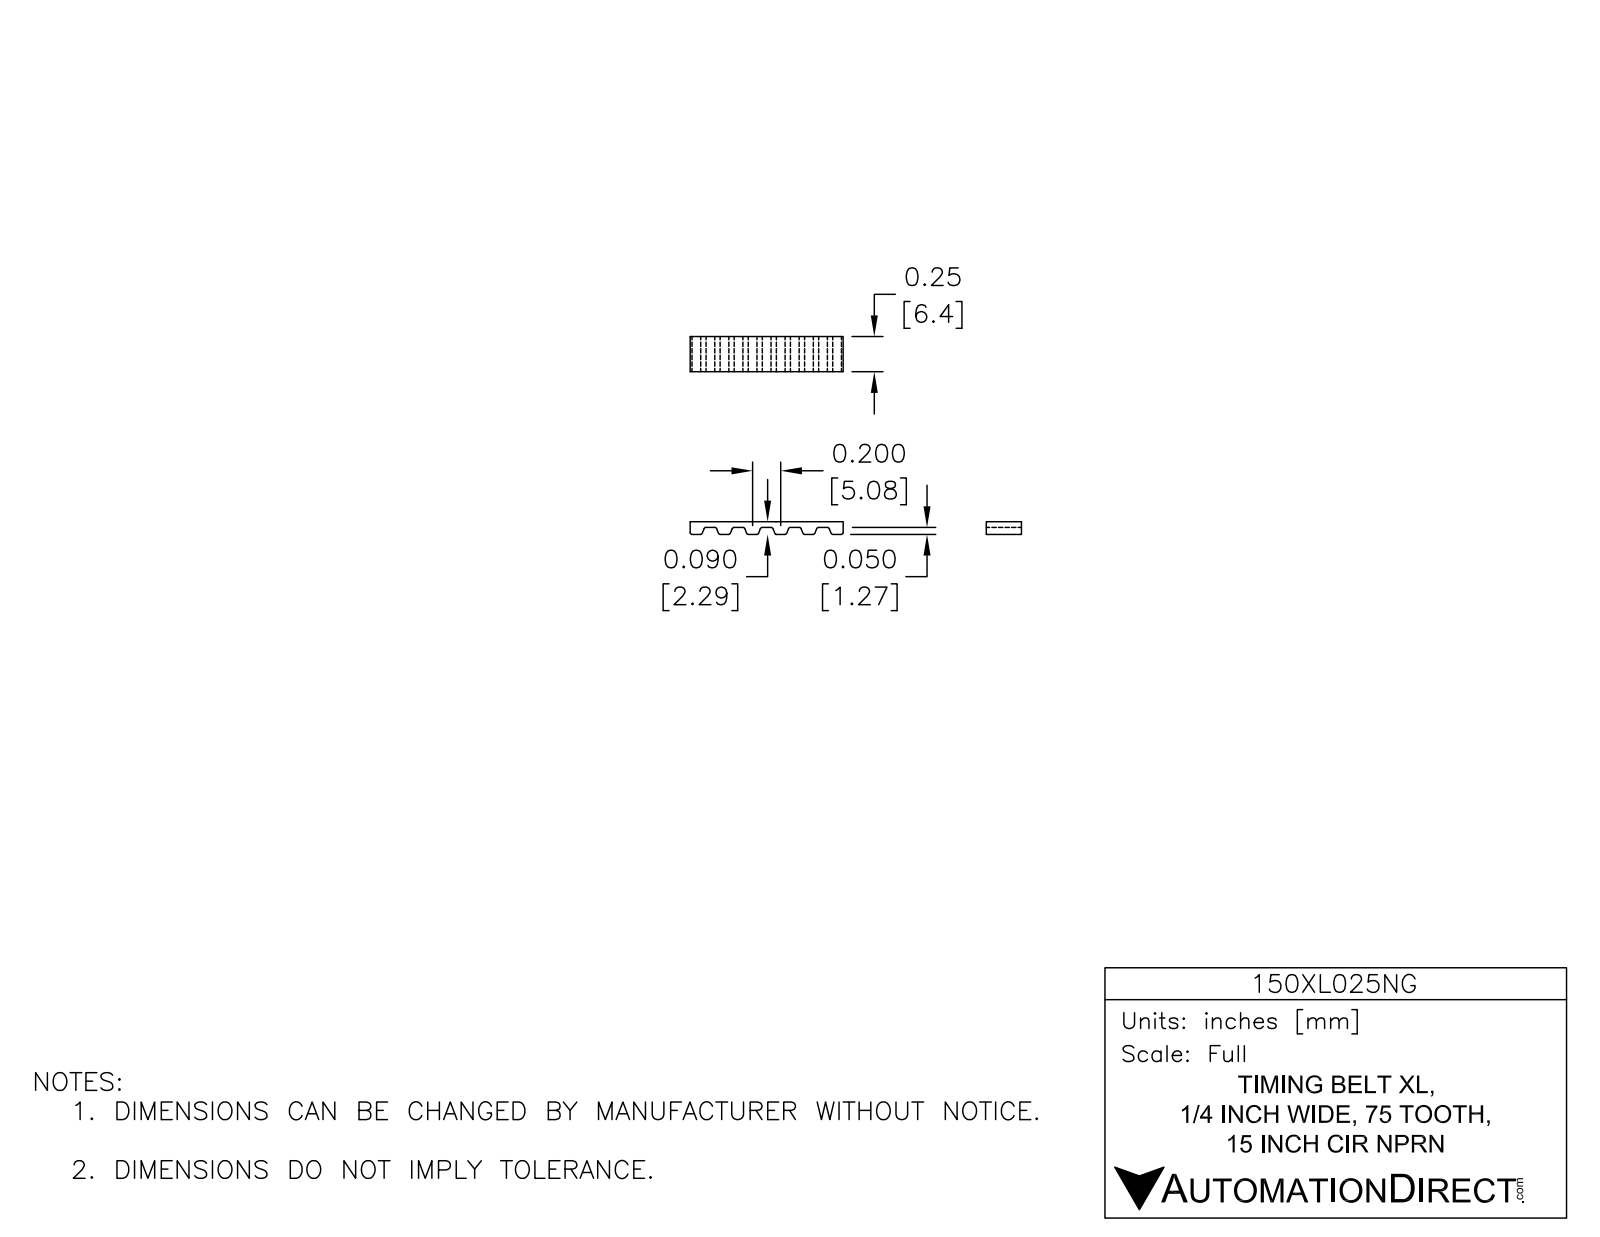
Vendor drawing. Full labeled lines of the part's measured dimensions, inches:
Part name (STEP PRODUCT): 150XL025NG
STEP written by: SolidWorks 2014 (AUTOMOTIVE_DESIGN)
Units: inches
Bodies: 1 solid, 640 faces (258 planar, 382 cylindrical, 0 other)
Overall size (bounding box): 5.788 × 3 × 0.25
Volume: 0.203 in³ · Surface area: 10.1 in²
Partial cylindrical surfaces — rounded edges, fillets, slot ends (radius × count): R0.015 ×300, R1.46 ×2, R1.5 ×2
Main face-to-face distances: 0.25, 3, 0.04, 2.96, 2.92, 0.356, 0.713, 0.535, 0.178, 1.069
